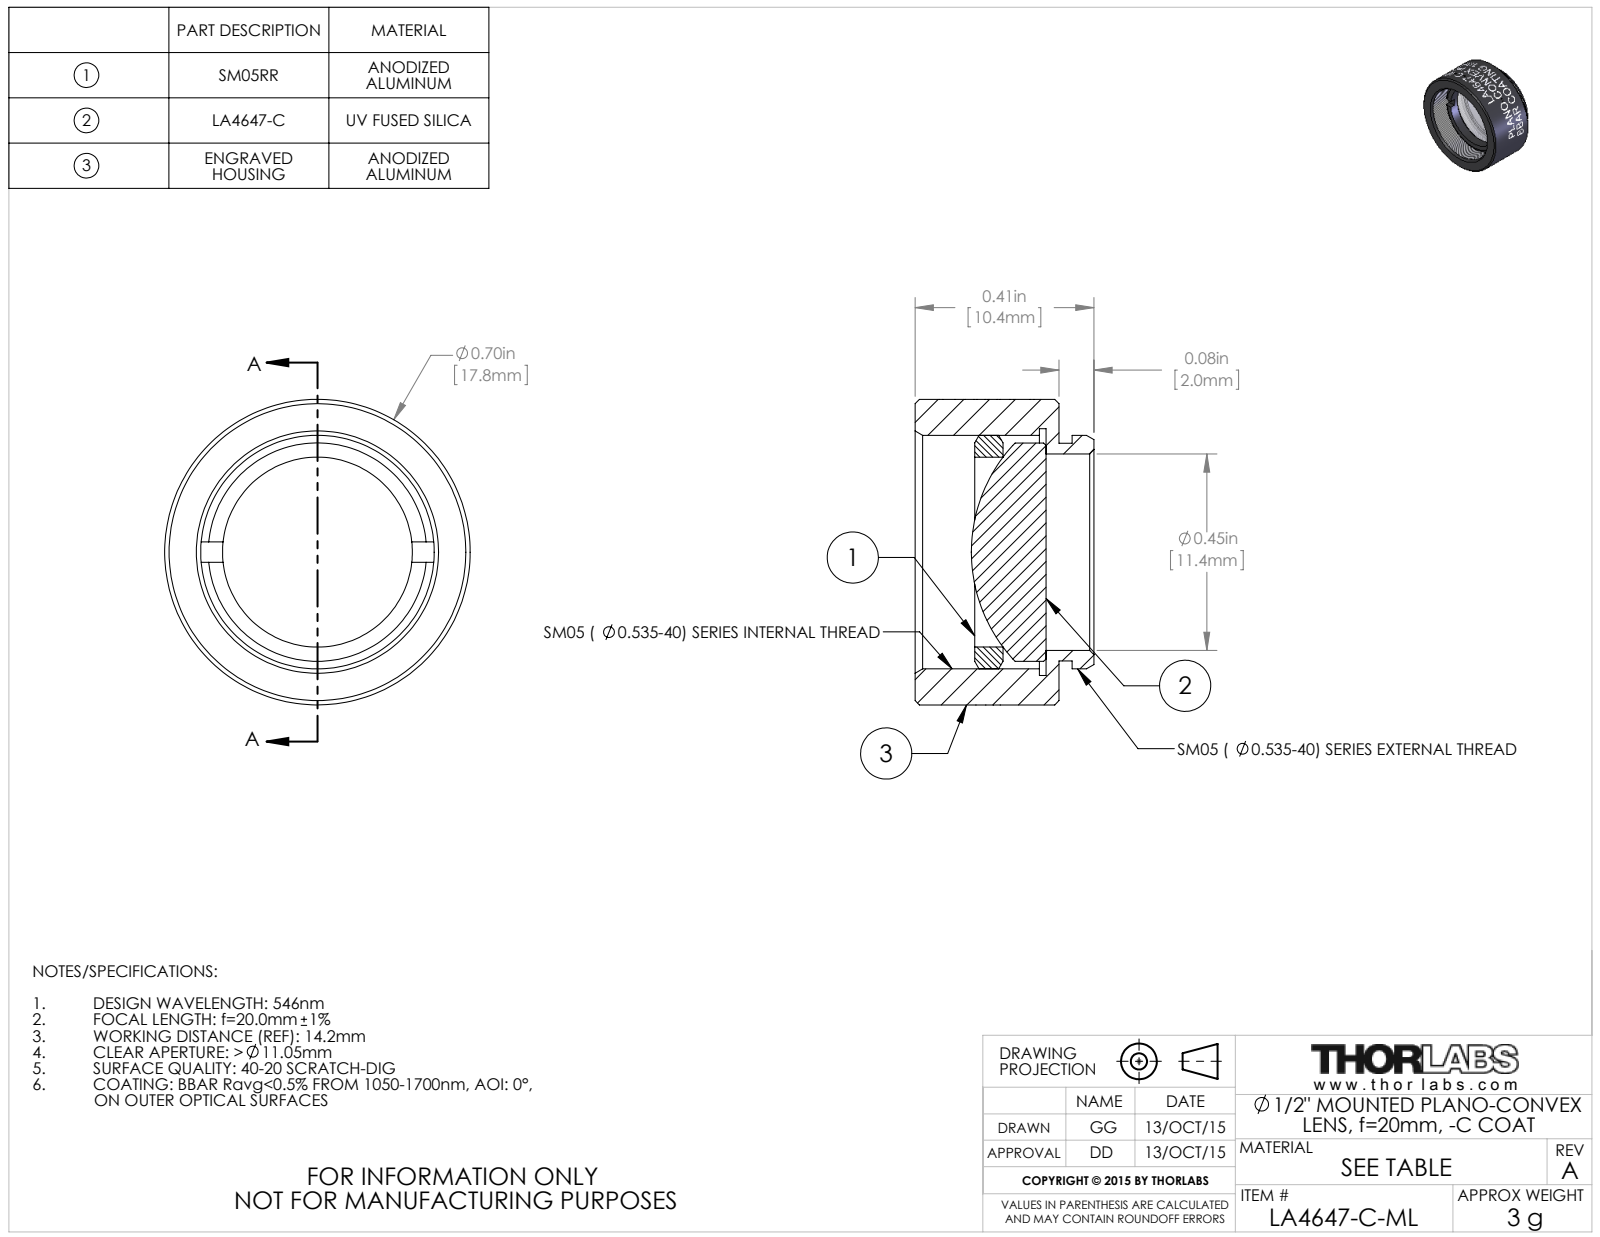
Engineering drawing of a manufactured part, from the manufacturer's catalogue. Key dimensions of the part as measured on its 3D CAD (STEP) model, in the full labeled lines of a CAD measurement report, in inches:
Part name (STEP PRODUCT): TTN039339-E0W
STEP written by: SolidWorks 2014 (CONFIG_CONTROL_DESIGN)
Units: inches
Bodies: 3 solids, 150 faces (16 planar, 113 cylindrical, 21 other)
Overall size (bounding box): 0.7 × 0.7 × 0.41
Volume: 0.087 in³ · Surface area: 2.877 in²
Round holes (diameter × count): ⌀0.435 ×1, ⌀0.45 ×1, ⌀0.535 ×1, ⌀0.565 ×1
Round bosses / shafts (diameter × count): ⌀0.7 ×1, ⌀0.535 ×1, ⌀0.5 ×1, ⌀0.499 ×1
Main face-to-face distances: 0.03, 0.33, 0.3, 0.128, 0.098, 0.202, 0.193, 0.163, 0.065, 0.137
